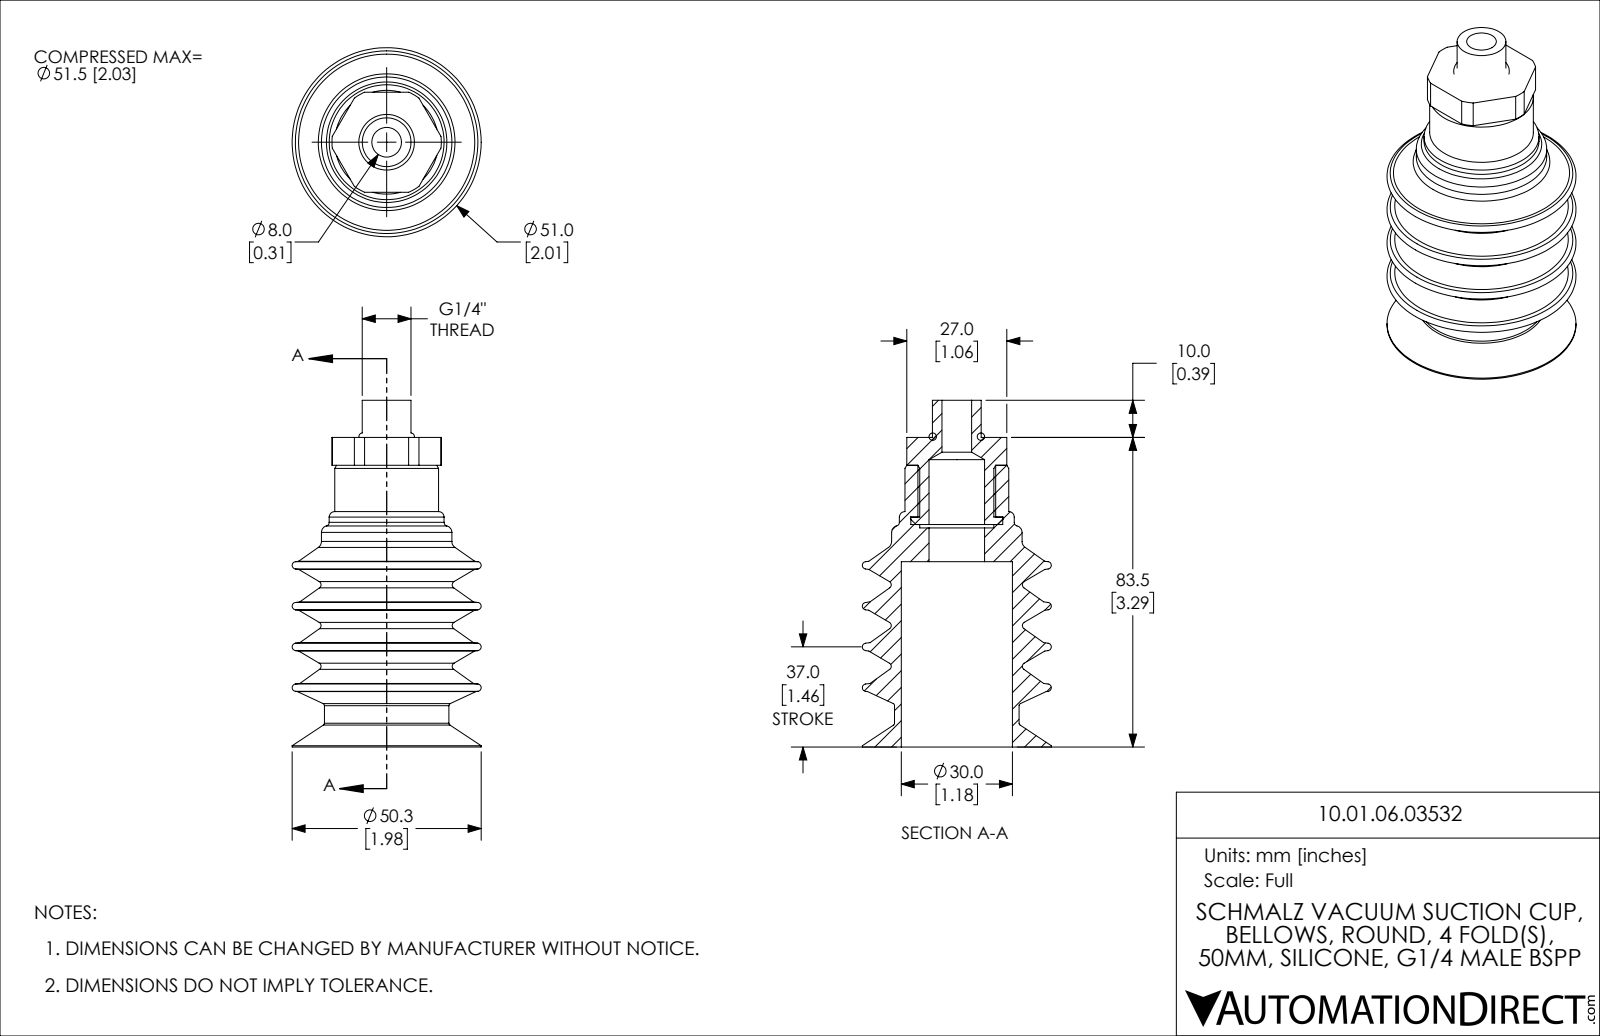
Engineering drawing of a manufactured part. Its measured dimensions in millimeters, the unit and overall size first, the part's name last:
Units: millimetres
Overall size (bounding box): 93.5 × 51 × 51
Round holes (diameter × count): ⌀8 ×1, ⌀15 ×1, ⌀20 ×1, ⌀24.8 ×1, ⌀30 ×1
Round bosses / shafts (diameter × count): ⌀51 ×1, ⌀35.2 ×1, ⌀33.6 ×1, ⌀31 ×1, ⌀28 ×1, ⌀25 ×1, ⌀21 ×1, ⌀13.16 ×1
Partial cylindrical surfaces — rounded edges, fillets, slot ends (radius × count): R14.75 ×1
Main face-to-face distances: 33.5, 50, 76, 26, 83.5, 7.5, 10, 60, 16, 23.5
Volume: 56 919 mm³ · Surface area: 28 805 mm²
Bodies: 3 solids, 132 faces (17 planar, 37 cylindrical, 78 other)
Part name (STEP PRODUCT): 10.01.06.03532
STEP written by: SolidWorks 2021 (CONFIG_CONTROL_DESIGN)
